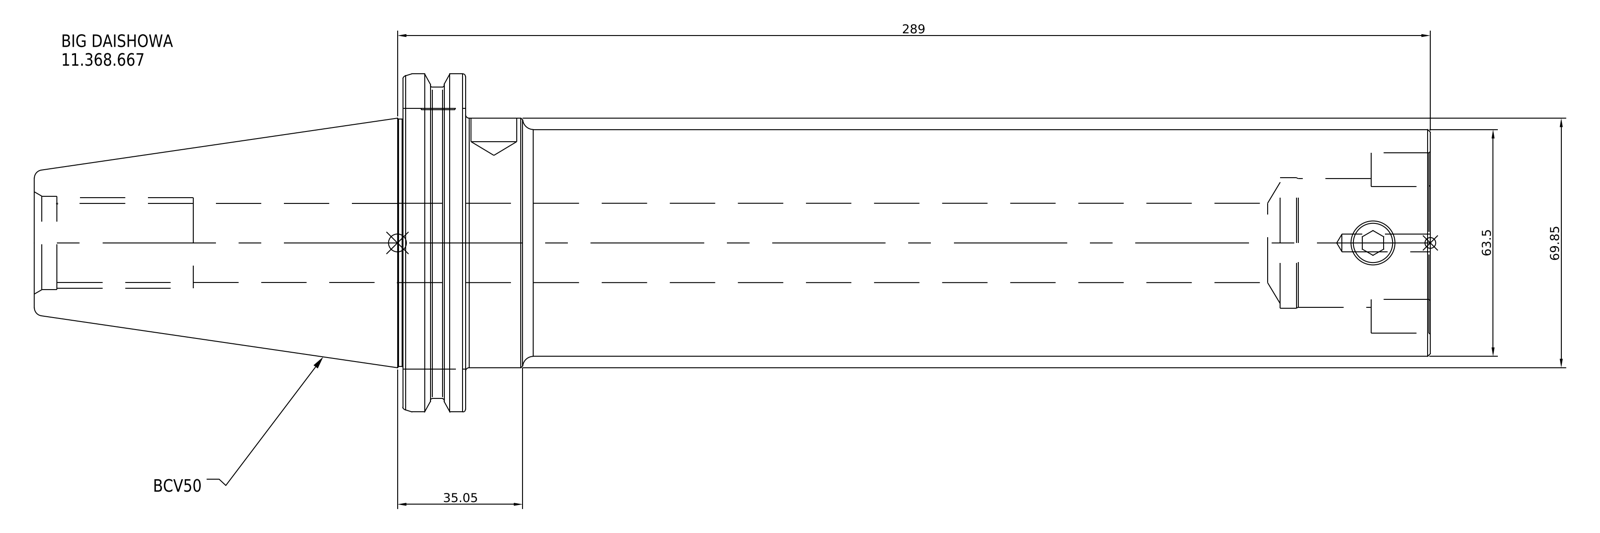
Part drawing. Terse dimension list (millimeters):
name: 11.368.667
written by: SolidWorks 2021 (CONFIG_CONTROL_DESIGN)
unit: mm
bodies: 1 solid, 16 faces (7 planar, 6 cylindrical, 3 other)
size: 390.6 × 98.43 × 98.43
volume: 1 247 000 mm³; area: 91 644 mm²
bosses: 1× ⌀98.43, 1× ⌀91.29, 1× ⌀69.85, 1× ⌀63.5
face distances: 17.55, 269.95, 287.5, 390.6, 120.65, 103.1, 254, 15.95, 33.5, 136.6
